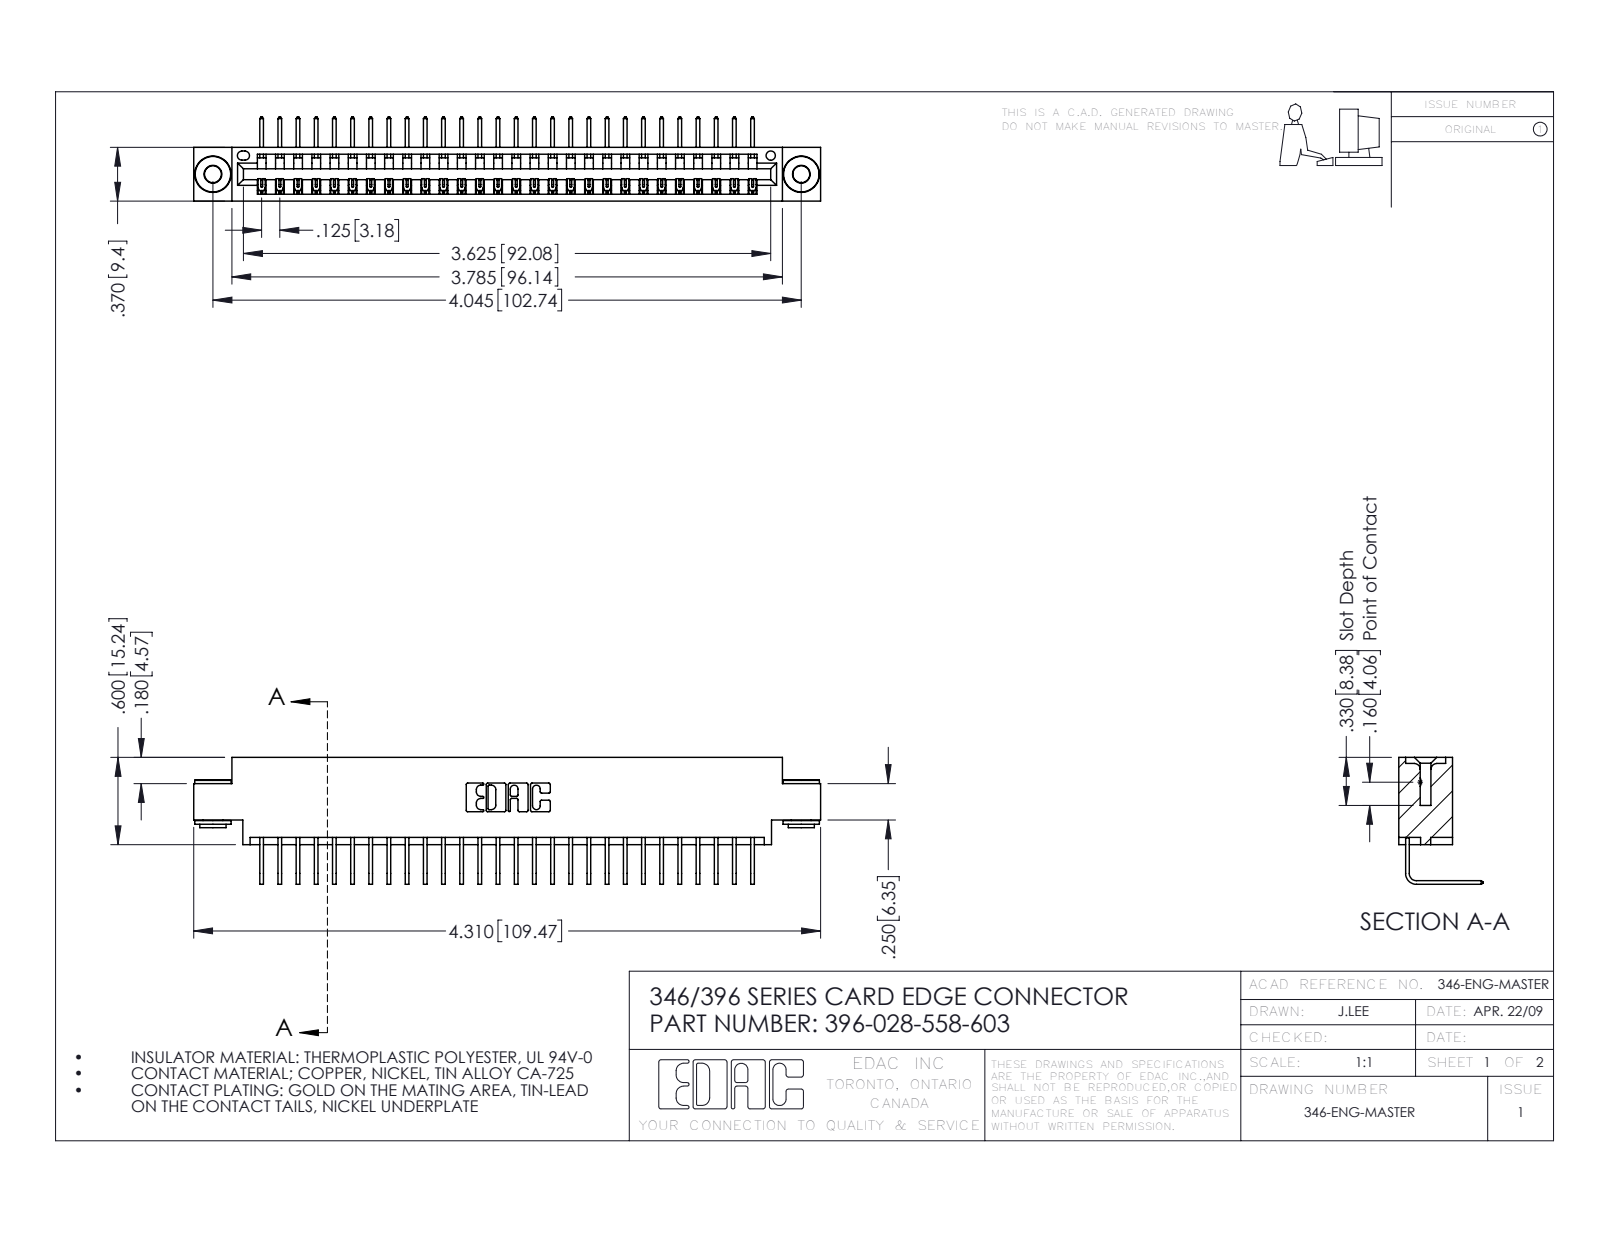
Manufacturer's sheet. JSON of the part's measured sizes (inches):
{"part_name": "396-028-558-603; 345-250-002_345-250-002-102; 345-292-001_558 Tail - 2; 346 Part_0.170 Offset - 0.156 Dia-TH", "step_written_by": "SolidWorks 2016 (CONFIG_CONTROL_DESIGN)", "units": "inches", "bodies": {"solids": 31, "faces": 1844, "planar": 1266, "cylindrical": 570, "other": 8}, "overall_size": [4.31, 0.873, 0.58], "volume_in3": 0.631, "surface_area_in2": 21.25, "round_holes": [[0.116, 2], [0.156, 2], [0.064, 1]], "round_bosses_or_shafts": [[0.25, 2], [0.18, 2], [0.136, 2]], "partial_cylinders_radius": [[0.006, 56], [0.01, 22], [0.007, 6], [0.031, 6], [0.026, 3], [0.031, 2], [0.04, 2], [0.014, 1]], "face_to_face_distances": [0.322, 0.048, 0.37, 0.25, 0.025, 0.298, 0.072, 0.148, 0.222, 0.1], "hole_center_spacings": [0.246, 3.837, 4.045]}
